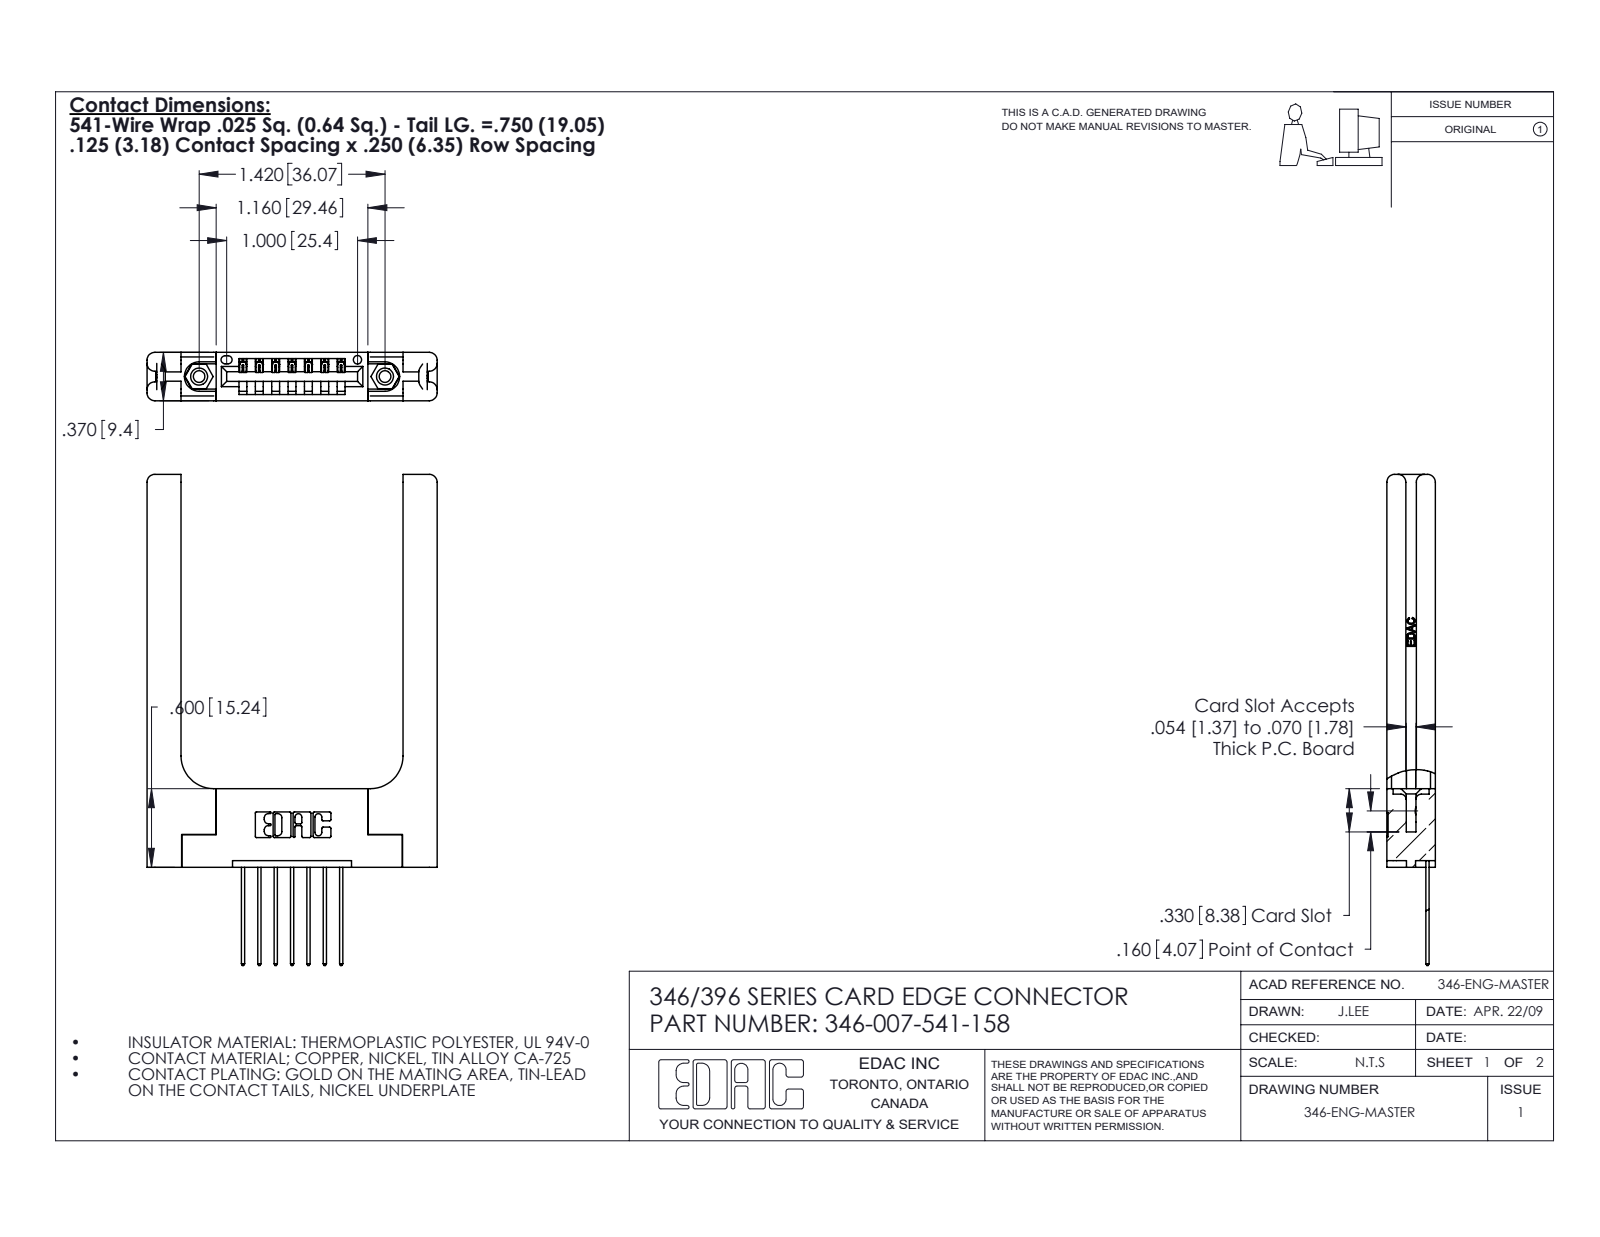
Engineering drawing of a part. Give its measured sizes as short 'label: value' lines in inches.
name: 346-007-541-158; 346-220-058_345-220-058; 345-292-001_345-293-141; 346 Part_Flush Mounting Lugs - 0.156 Dia-TH (+1 more)
written by: SolidWorks 2020 (CONFIG_CONTROL_DESIGN)
unit: in
bodies: 12 solids, 798 faces (518 planar, 220 cylindrical, 60 other)
size: 3.75 × 2.216 × 0.37
volume: 0.773 in³; area: 17.67 in²
holes: 2× ⌀0.089, 2× ⌀0.125, 2× ⌀0.156, 1× ⌀0.064
bosses: 2× ⌀0.155
rounds: 22× R0.01, 16× R0.06, 14× R0.006, 14× R0.01, 6× R0.007, 6× R0.031, 3× R0.026, 2× R0.03
face distances: 0.37, 0.15, 0.22, 0.072, 0.148, 0.25, 0.048, 0.322, 0.102, 0.173
hole spacings: 0.246, 1.217, 1.42
